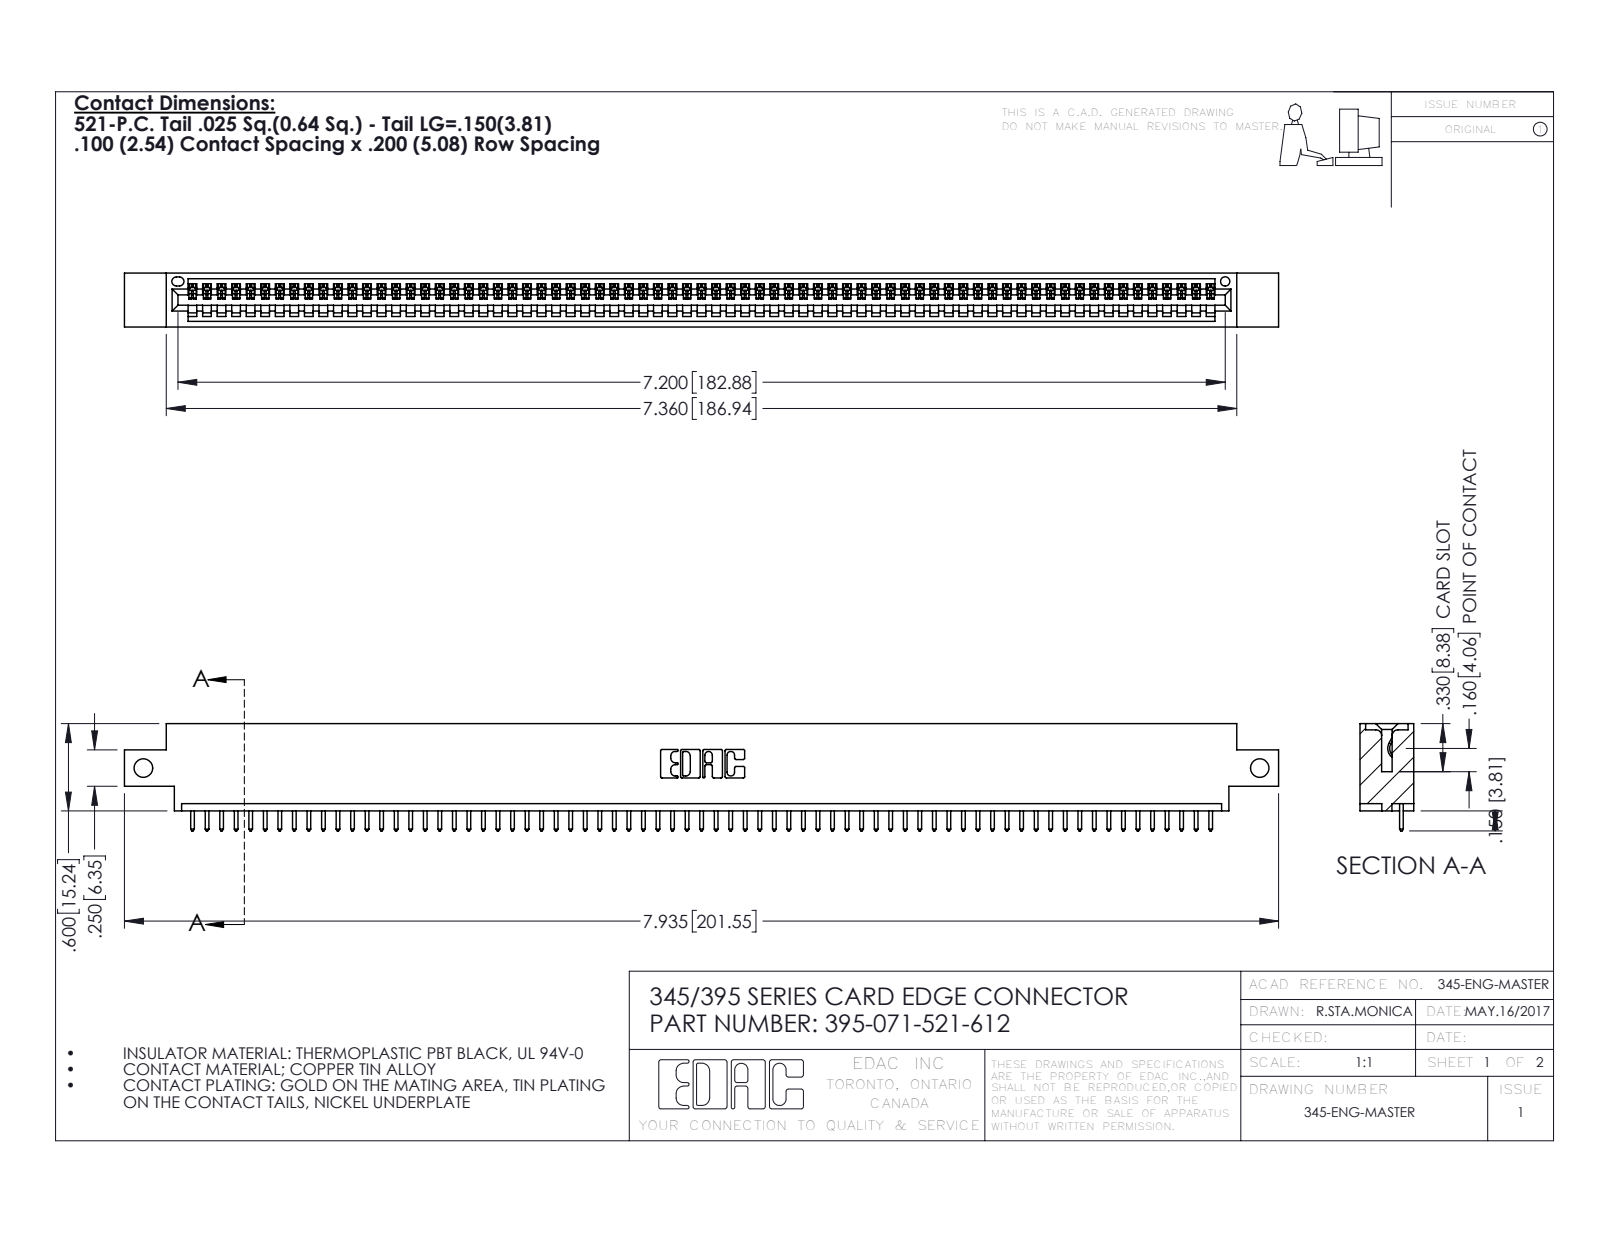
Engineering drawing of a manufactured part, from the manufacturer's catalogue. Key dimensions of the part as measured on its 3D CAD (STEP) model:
Part name (STEP PRODUCT): 395-071-521-612; 345-292-001_345-293-121; 345 Part_0.170 Offset - Side Mount
STEP written by: SolidWorks 2016 (CONFIG_CONTROL_DESIGN)
Units: inches
Bodies: 72 solids, 4248 faces (2924 planar, 1324 cylindrical, 0 other)
Overall size (bounding box): 7.935 × 0.737 × 0.37
Volume: 1.158 in³ · Surface area: 38.45 in²
Round holes (diameter × count): ⌀0.128 ×2, ⌀0.064 ×1
Partial cylindrical surfaces — rounded edges, fillets, slot ends (radius × count): R0.006 ×142, R0.01 ×142, R0.01 ×22, R0.007 ×6, R0.031 ×6, R0.026 ×3, R0.031 ×2, R0.04 ×2
Main face-to-face distances: 0.298, 0.072, 0.37, 0.2, 0.098, 0.272, 0.025, 0.225, 0.175, 0.149
Hole centre spacings: 7.675
